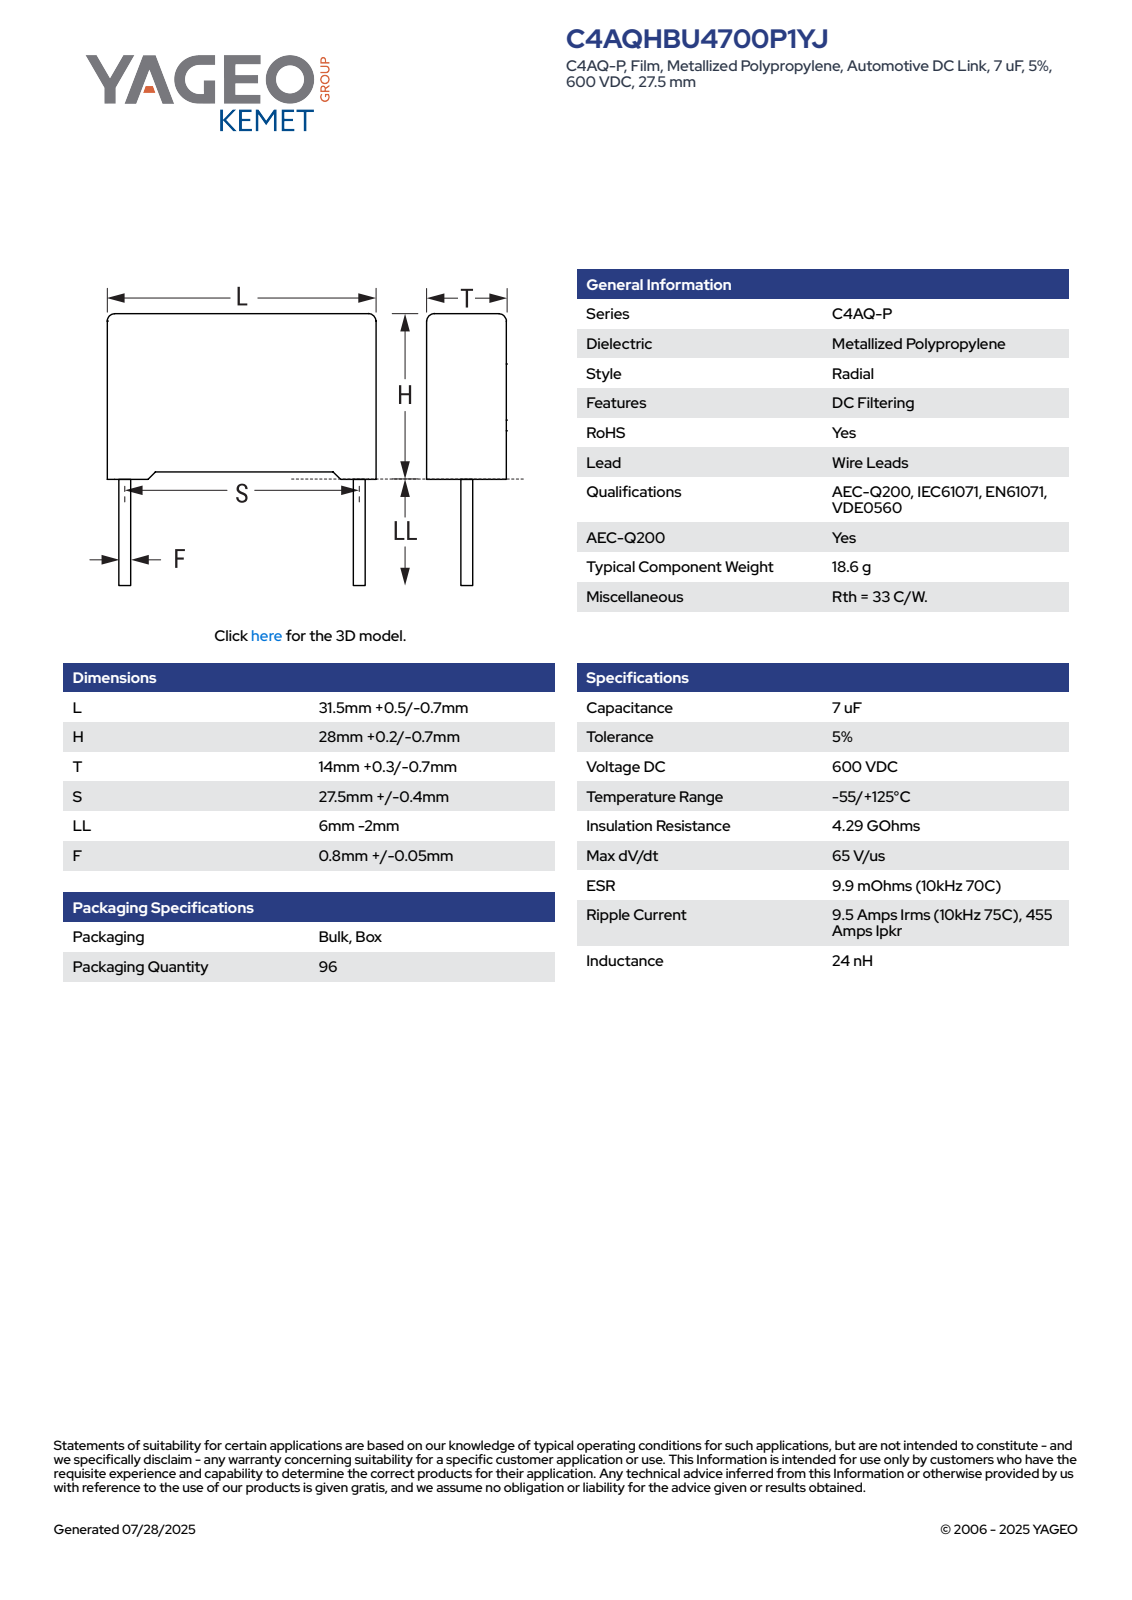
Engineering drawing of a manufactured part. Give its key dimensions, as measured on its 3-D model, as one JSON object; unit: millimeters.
{"part_name": "CFR_RB2CFP_31.5X28X14_L32H28.2T14.3S27.5LL4F0.85", "step_written_by": "SolidWorks 2014 (AUTOMOTIVE_DESIGN)", "units": "millimeters", "bodies": {"solids": 4, "faces": 85, "planar": 77, "cylindrical": 8, "other": 0}, "overall_size": [32.2, 32, 14.3], "volume_mm3": 12521, "surface_area_mm2": 3594, "round_bosses_or_shafts": [[0.85, 2]], "partial_cylinders_radius": [[0.5, 4]], "face_to_face_distances": [14.3, 32, 27.23, 27.45, 0.75, 0.97, 28.2, 1.07, 30.93, 29.86]}
